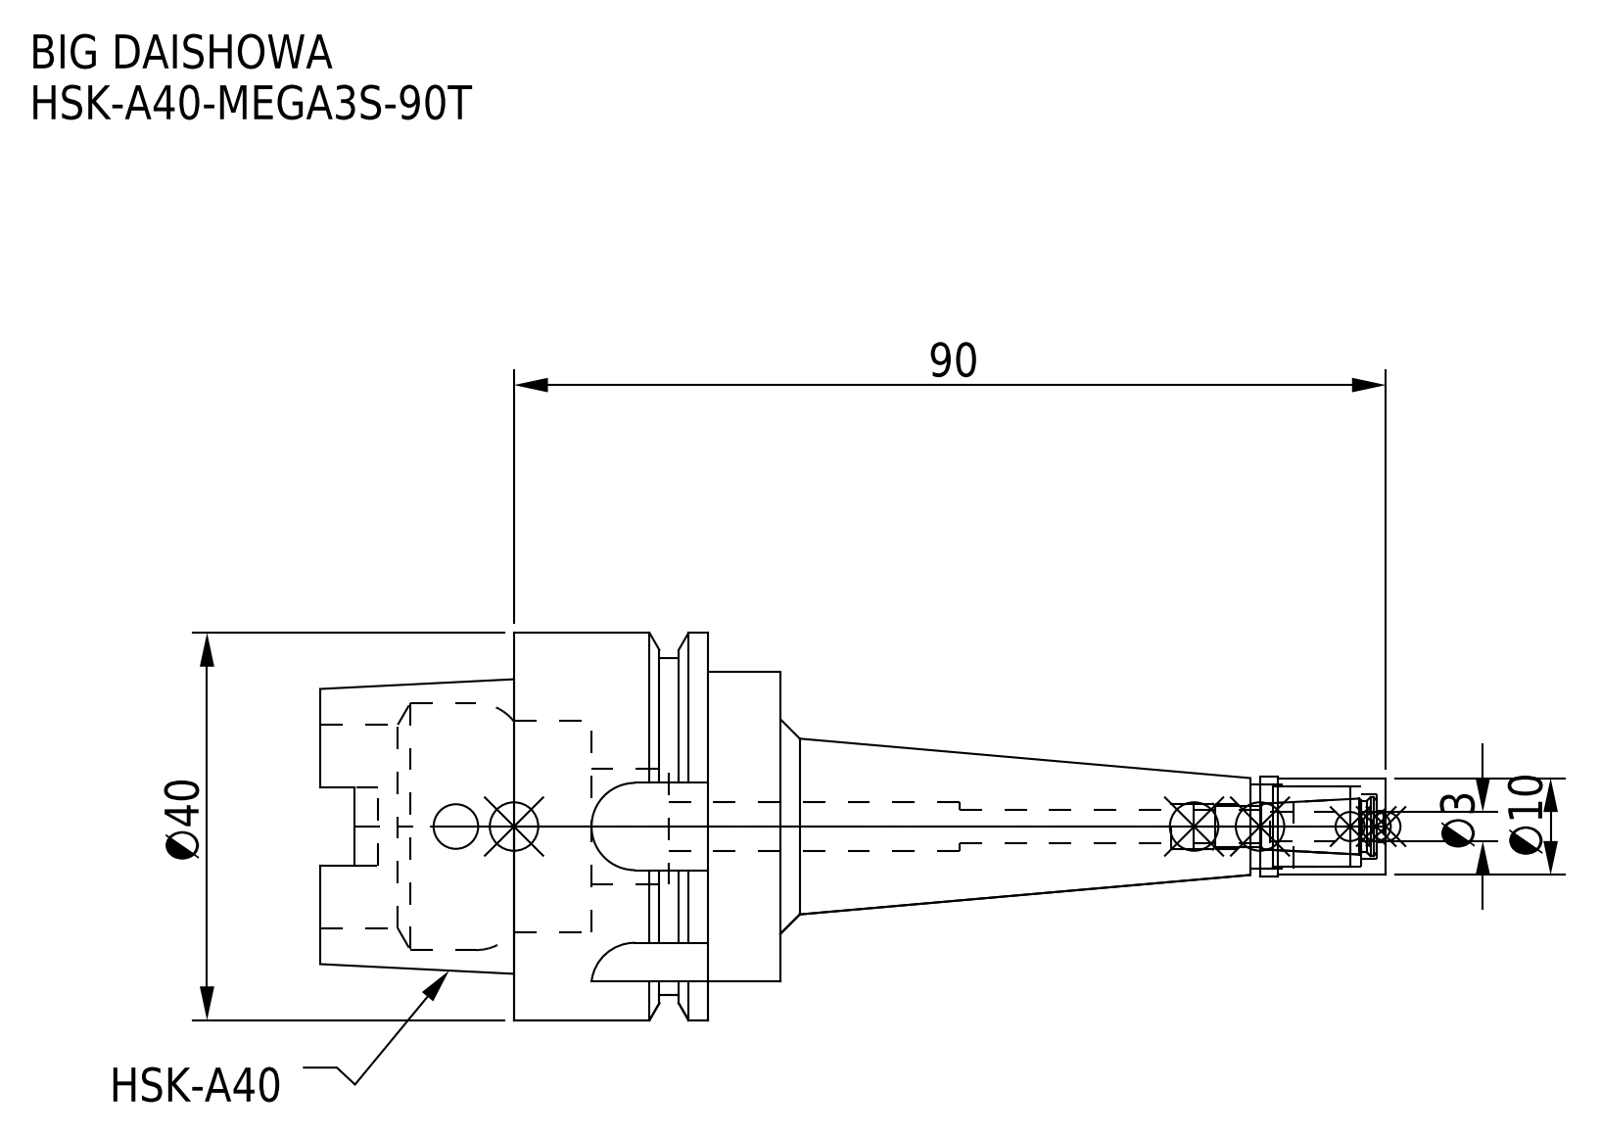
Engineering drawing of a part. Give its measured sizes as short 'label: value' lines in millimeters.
name: HSK-A40-MEGA3S-90T-030.stp; HA40MS03090T-030_ASM.stp; HSK-A40-MEGA3S-90T; HSK-A40-MEGA3S-90T_1.stp (+3 more)
written by: SolidWorks 2019 (CONFIG_CONTROL_DESIGN)
unit: mm
bodies: 2 solids, 123 faces (47 planar, 54 cylindrical, 22 other)
size: 110 × 40 × 40
volume: 38 336 mm³; area: 14 311 mm²
holes: 1× ⌀3.3, 1× ⌀3.4, 1× ⌀4.6, 1× ⌀4.7, 1× ⌀5, 1× ⌀6.6, 1× ⌀8.2, 1× ⌀8.7, 1× ⌀12, 1× ⌀21, 1× ⌀21.8, 1× ⌀25.5
bosses: 1× ⌀40, 1× ⌀34.8, 1× ⌀32, 1× ⌀10.3, 1× ⌀10
rounds: 4× R1.88, 4× R4.5
face distances: 20, 27.5, 7.5, 19.55, 12.05, 7.95, 47.5, 40, 27.95, 34
